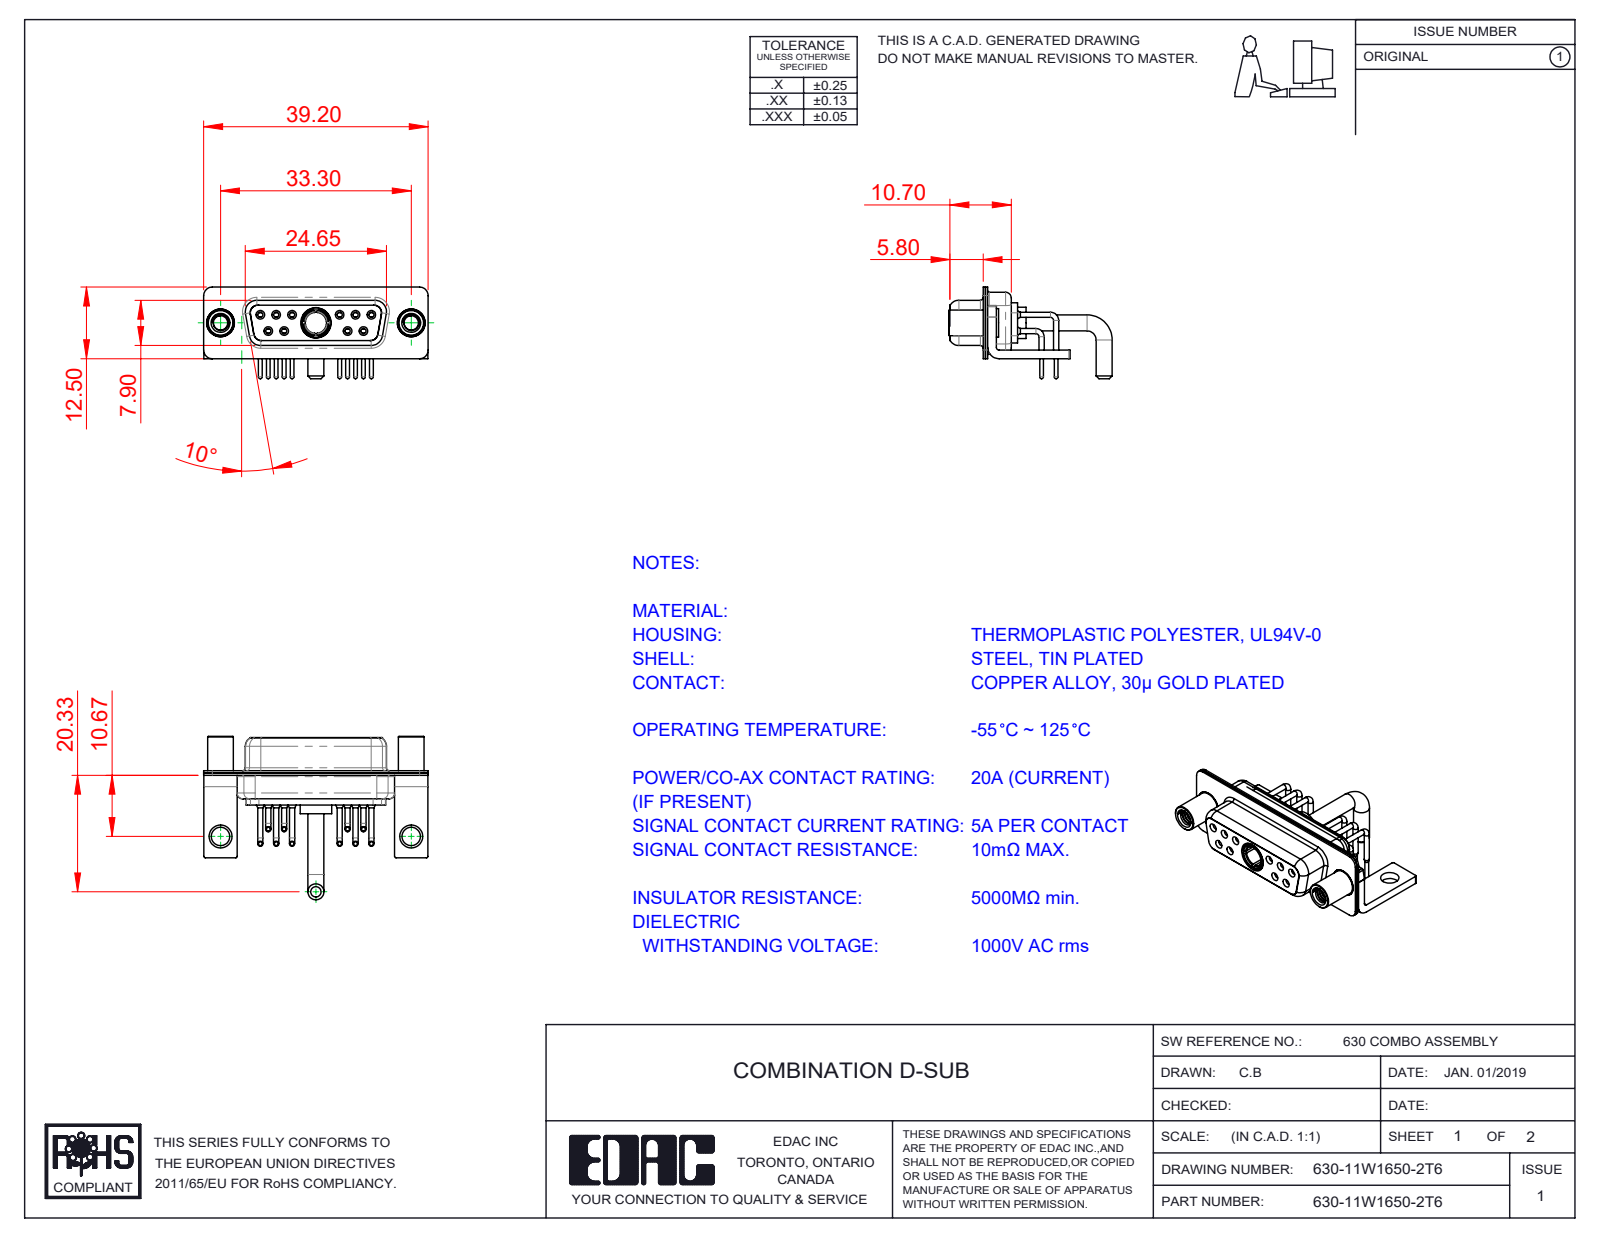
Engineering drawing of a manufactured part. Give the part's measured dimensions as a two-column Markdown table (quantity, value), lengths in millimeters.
| quantity | value |
| --- | --- |
| part name | 630Combo Stabilizer Bracket; 630Combo Shell Rear_15 Contacts; 630Combo Contact Row 2; 630Combo Housing_11W1 (+5 more) |
| STEP written by | SolidWorks 2020 (CONFIG_CONTROL_DESIGN) |
| units | millimeters |
| bodies | 19 solids, 985 faces (268 planar, 464 cylindrical, 253 other) |
| overall size | 39.2 × 28.53 × 16 |
| volume | 3 074 mm³ |
| surface area | 7 259 mm² |
| round holes (diameter × count) | 0.9 × 10, 1.1 × 10, 1.5 × 10, 2 × 10, 1.7 × 6, 1.6 × 4, 4.85 × 3, 2.5 × 2, 3.2 × 2, 4 × 2, 4.05 × 2, 3.7 × 1 |
| round bosses / shafts (diameter × count) | 0.9 × 10, 0.65 × 10, 1.6 × 6, 5 × 2, 4.95 × 2, 4.8 × 2, 4.5 × 2, 2.8 × 2 |
| partial cylindrical surfaces (radius × count) | 0.25 × 16, 1.5 × 16, 2 × 13, 1.35 × 12, 1.6 × 8, 0.5 × 5, 0.6 × 4, 0.65 × 4 |
| main face-to-face distances | 0.4, 0.8, 1.4, 0.45, 8.45, 1.5, 1.8, 8.9, 6.2, 2.3 |
| hole center spacings | 3.16, 2.77, 13.85, 11.08, 16.62, 5.03, 5.04, 5.54 |
